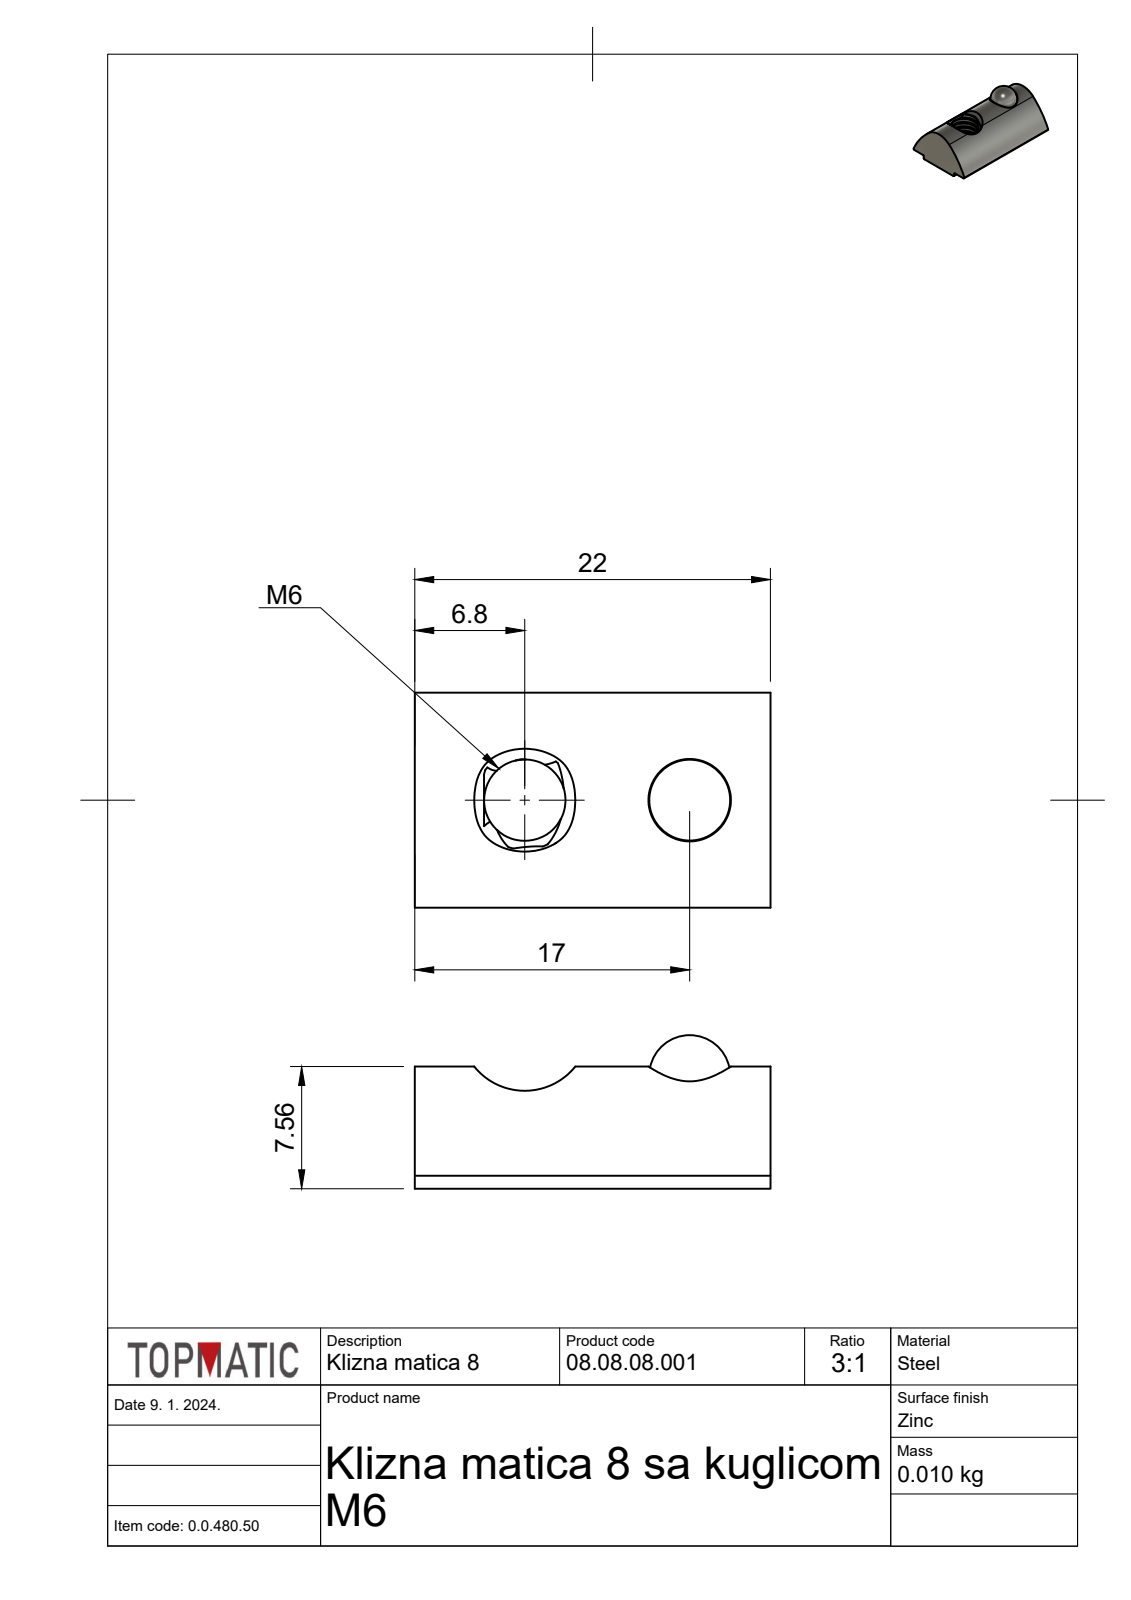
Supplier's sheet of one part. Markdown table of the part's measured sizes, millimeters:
| quantity | value |
| --- | --- |
| part name | Klizna matica 8 M6 v1 |
| STEP written by | Autodesk Translation Framework v12.14.0.127 (AUTOMOTIVE_DESIGN) |
| units | millimeters |
| bodies | 2 solids, 45 faces (8 planar, 29 cylindrical, 8 other) |
| overall size | 22 × 13.3 × 9.5 |
| volume | 1 258 mm³ |
| surface area | 1 180 mm² |
| round holes (diameter × count) | 5.04 × 1, 5.1 × 1, 6.15 × 1 |
| partial cylindrical surfaces (radius × count) | 0.2 × 6, 4 × 2, 16 × 2 |
| main face-to-face distances | 0.8, 22, 8, 6.15, 6.95 |
| hole center spacings | 10.2 |
